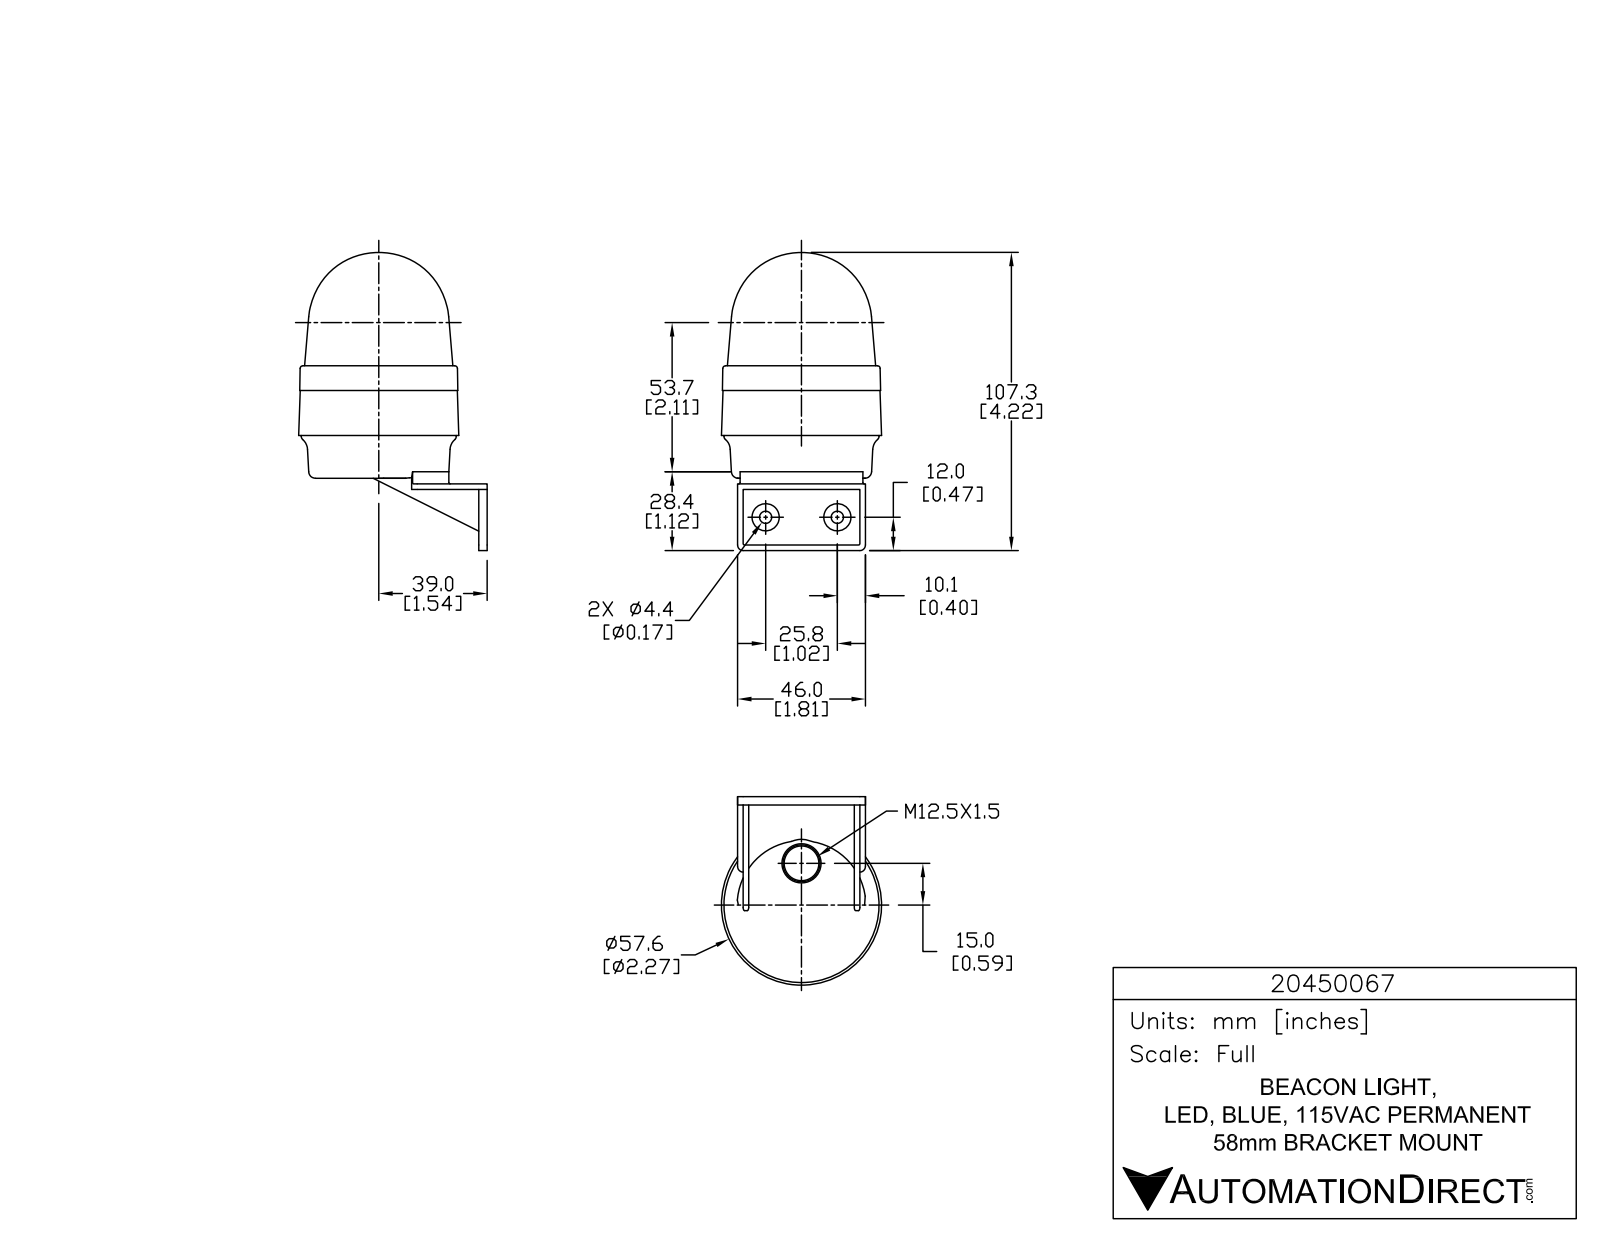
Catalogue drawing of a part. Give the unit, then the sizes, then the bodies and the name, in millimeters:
Units: millimetres
Overall size (bounding box): 107.3 × 72.4 × 61.1
Round holes (diameter × count): ⌀1 ×3, ⌀4.4 ×2
Round bosses / shafts (diameter × count): ⌀5.7 ×3, ⌀1.4 ×3, ⌀9.8 ×2, ⌀55.8 ×1
Partial cylindrical surfaces — rounded edges, fillets, slot ends (radius × count): R0.2 ×6, R0.2 ×6, R0.2 ×6, R0.5 ×6, R3.3 ×6, R2 ×4, R0.1 ×3, R0.1 ×3
Main face-to-face distances: 2, 4, 40, 42, 1, 3, 38, 22, 24, 19.4
Hole centre spacings: 25.8
Volume: 168 300 mm³ · Surface area: 21 540 mm²
Bodies: 1 solid, 828 faces (551 planar, 179 cylindrical, 98 other)
Part name (STEP PRODUCT): 20450067
STEP written by: SolidWorks 2015 (AUTOMOTIVE_DESIGN)
